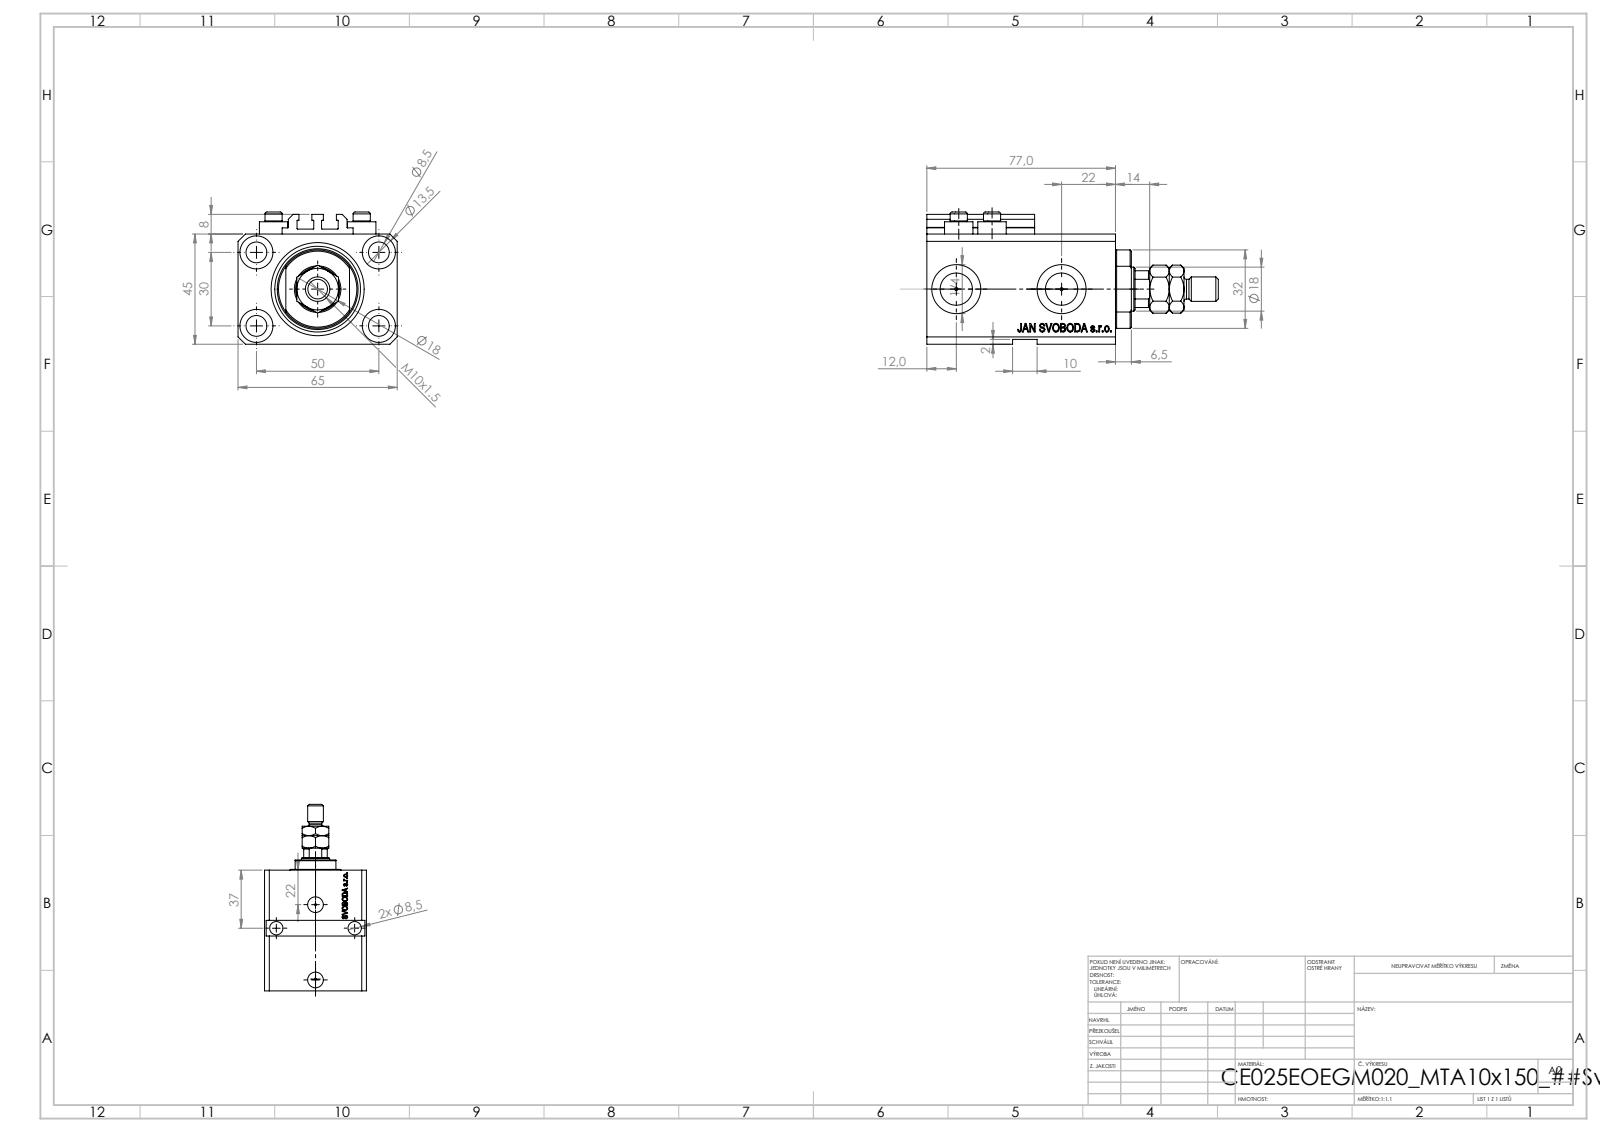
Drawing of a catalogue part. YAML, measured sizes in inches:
part_name: "V250CE_E_Body; V250CE_VC_E; MTA; ALLEN BOLT V250CE (+1 more)"
step_written_by: "SolidWorks 2019 (CONFIG_CONTROL_DESIGN)"
units: inches
bodies: {solids: 9, faces: 1116, planar: 526, cylindrical: 130, other: 460}
overall_size: [4.685, 2.559, 2.126]
volume: 12.46
surface_area: 94.43
round_holes:
  - {diameter: 0.335, count: 7}
  - {diameter: 0.049, count: 4}
  - {diameter: 0.157, count: 4}
  - {diameter: 0.531, count: 4}
  - {diameter: 0.394, count: 2}
  - {diameter: 0.518, count: 2}
  - {diameter: 0.787, count: 2}
  - {diameter: 0.709, count: 1}
  - {diameter: 0.984, count: 1}
  - {diameter: 1.496, count: 1}
round_bosses_or_shafts:
  - {diameter: 0.457, count: 4}
  - {diameter: 0.276, count: 4}
  - {diameter: 0.394, count: 1}
  - {diameter: 0.315, count: 1}
partial_cylinders:
  - {radius: 0.008, count: 10}
  - {radius: 0.335, count: 1}
  - {radius: 0.63, count: 1}
face_to_face_distances: [1.772, 2.559, 0.551, 2.48, 3.031, 0.079, 0.272, 2.209, 2.76, 0.807]
hole_center_spacings: [1.148, 1.969, 0.535, 0.595, 0.741, 0.747, 1.032, 1.048]
